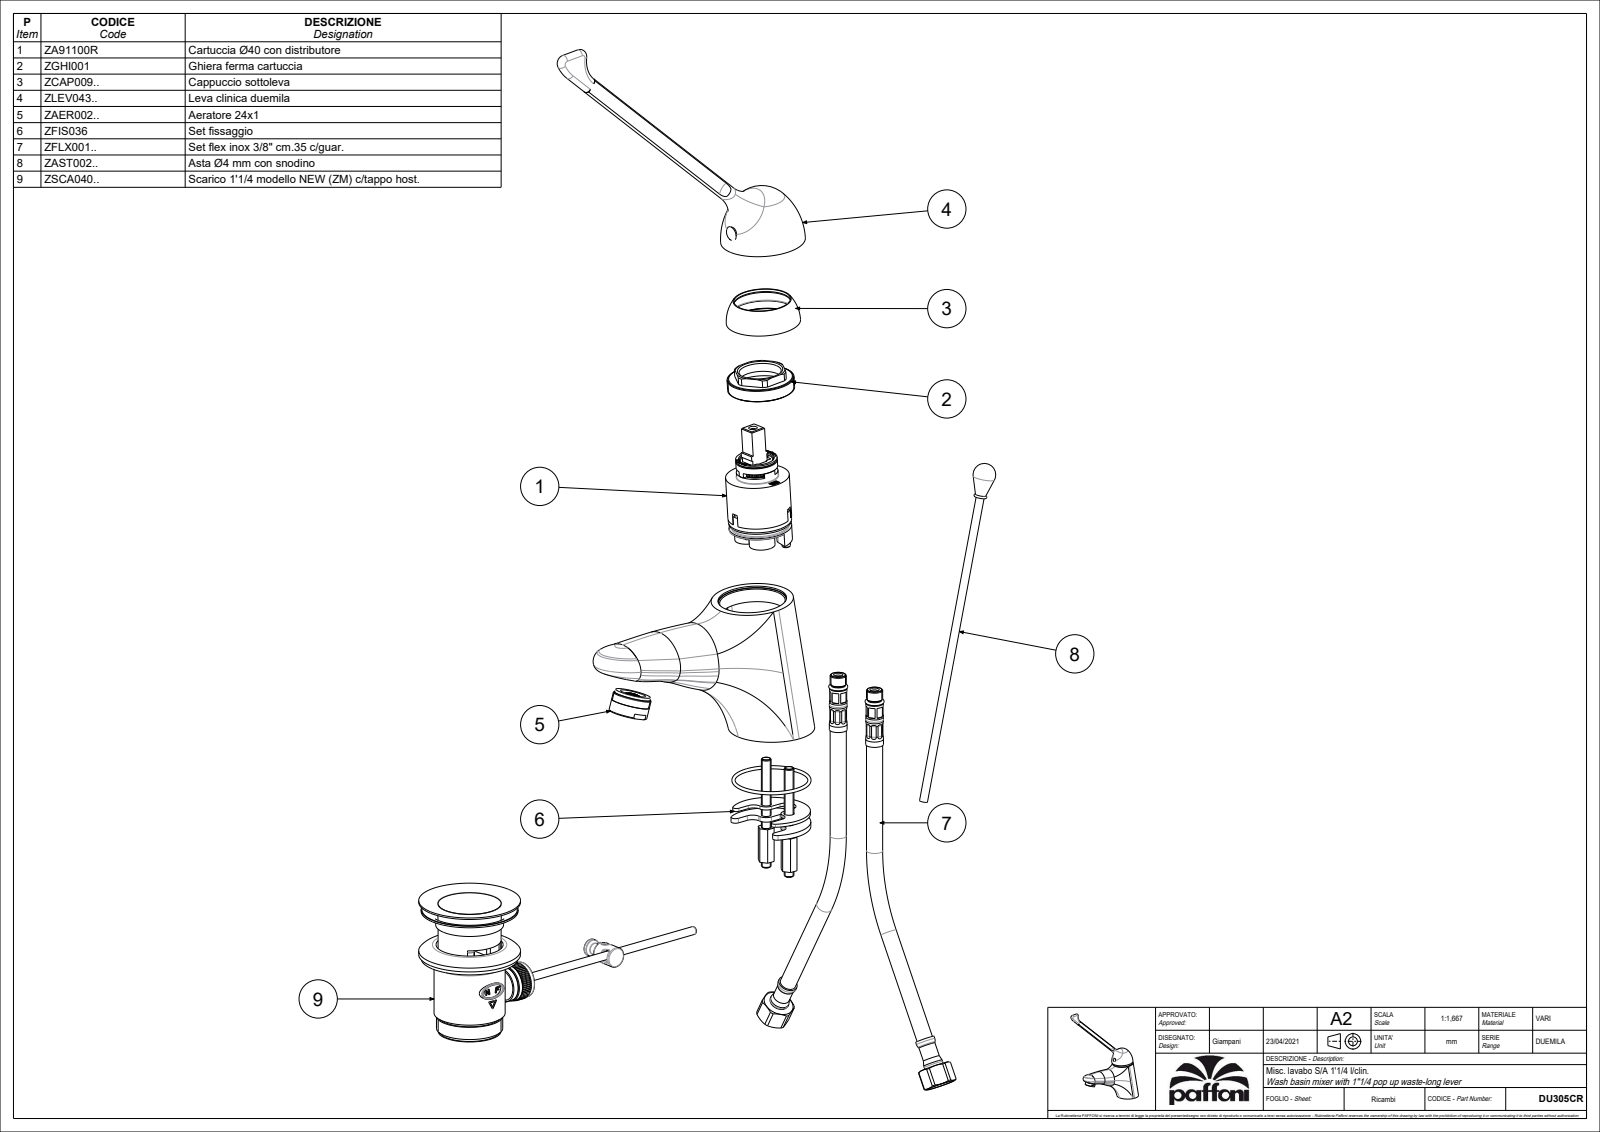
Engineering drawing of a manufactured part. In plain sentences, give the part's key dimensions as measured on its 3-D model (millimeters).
The part is named "DU305CR". Its 3-D file was written by "CREO PARAMETRIC BY PTC INC, 2020044 (CONFIG_CONTROL_DESIGN)". It is 6 solids with 2658 faces: 1975 planar, 365 cylindrical and 318 other. Overall it measures 253.92 by 217.51 by 53.5 millimeters. Its volume is 317 778 cubic millimeters and its surface area 89 395 square millimeters. Round holes: 4 of diameter 8, 3 of diameter 11, 2 of diameter 4.6, 2 of diameter 5.5, 2 of diameter 7, 2 of diameter 9, 2 of diameter 12, 2 of diameter 21, 1 of diameter 3.3, 1 of diameter 4, 1 of diameter 5, 1 of diameter 6. Round bosses or shafts: 3 of diameter 10, 2 of diameter 15.9, 2 of diameter 9.4, 2 of diameter 8.2, 2 of diameter 6, 2 of diameter 5, 1 of diameter 44.5, 1 of diameter 39.5. Partial cylindrical surfaces (rounded edges, fillets, slot ends): 53 of radius 0.5, 24 of radius 0.2, 4 of radius 0.3, 4 of radius 1.5, 2 of radius 3, 2 of radius 5.5, 2 of radius 7.5, 1 of radius 4. The main face-to-face distances are 6, 8, 4, 4.8, 5, 10.8, 1, 2, 0.5, 1.3. The hole center spacings are 9.9, 8.61, 6, 2, 8.6, 10.97, 13.04, 14.
